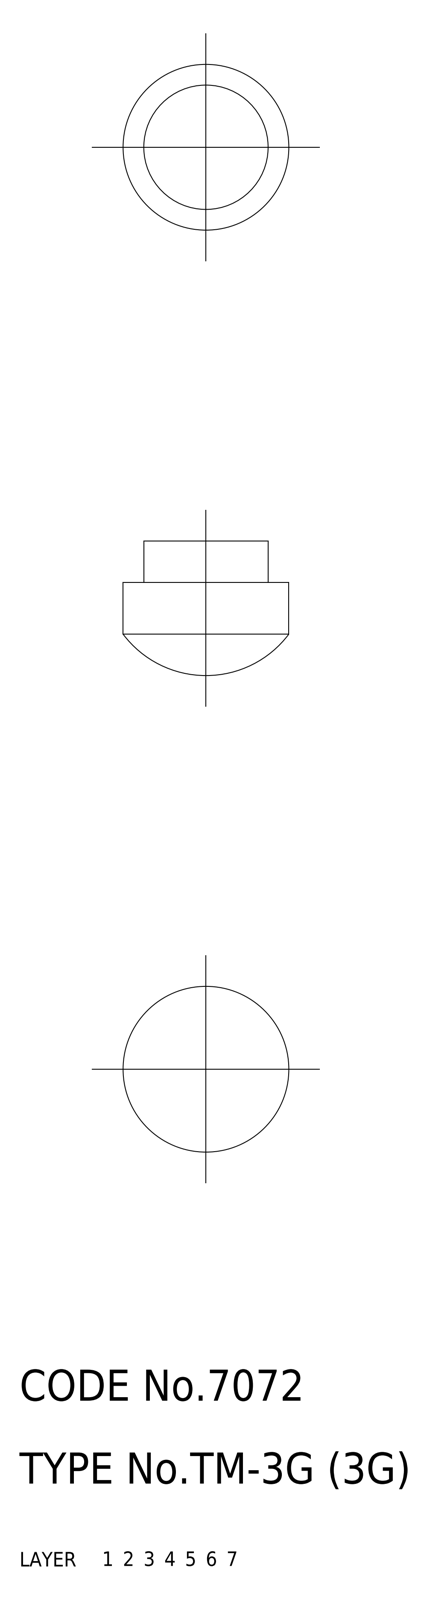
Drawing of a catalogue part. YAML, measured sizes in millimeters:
part_name: "rubber foot"
step_written_by: "CADfix (AUTOMOTIVE_DESIGN)"
units: millimeters
bodies: {solids: 1, faces: 7, planar: 0, cylindrical: 0, other: 7}
overall_size: [16, 16, 13]
volume: 1896
surface_area: 855
